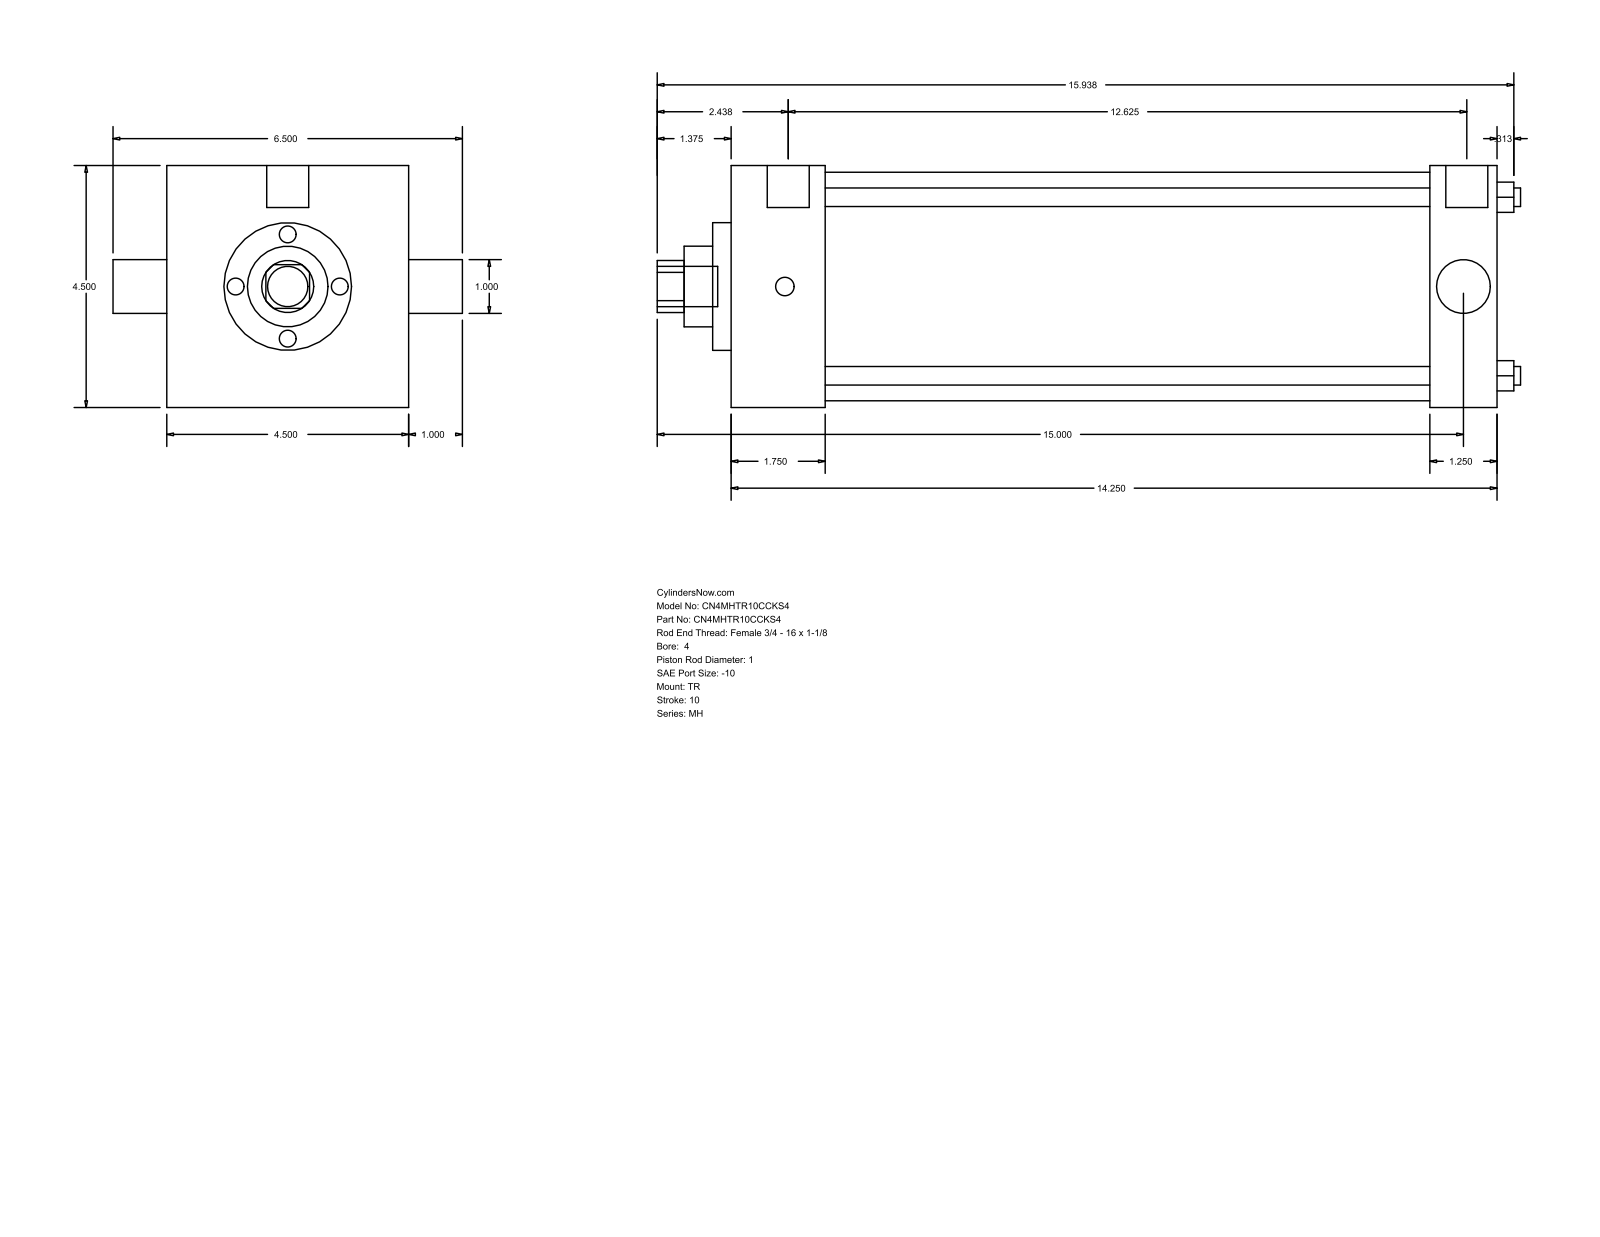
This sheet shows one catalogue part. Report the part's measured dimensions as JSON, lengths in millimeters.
{"part_name": "MH_TR__0400_1", "step_written_by": "GSSL Pune (CONFIG_CONTROL_DESIGN)", "units": "millimeters", "bodies": {"solids": 0, "faces": 86, "planar": 61, "cylindrical": 25, "other": 0}, "overall_size": [407.99, 165.1, 114.3], "round_holes": [[8.76, 4], [25.4, 2], [38.1, 1], [60.33, 1], [107.95, 1]], "round_bosses_or_shafts": [[8.73, 3], [19.84, 2], [19.05, 1]], "partial_cylinders_radius": [[12.29, 1]], "face_to_face_distances": [114.3, 361.96, 44.46, 317.5, 330.2, 285.74, 31.76, 8.73, 53.19, 338.93], "hole_center_spacings": [59.62, 84.32, 119.25]}
